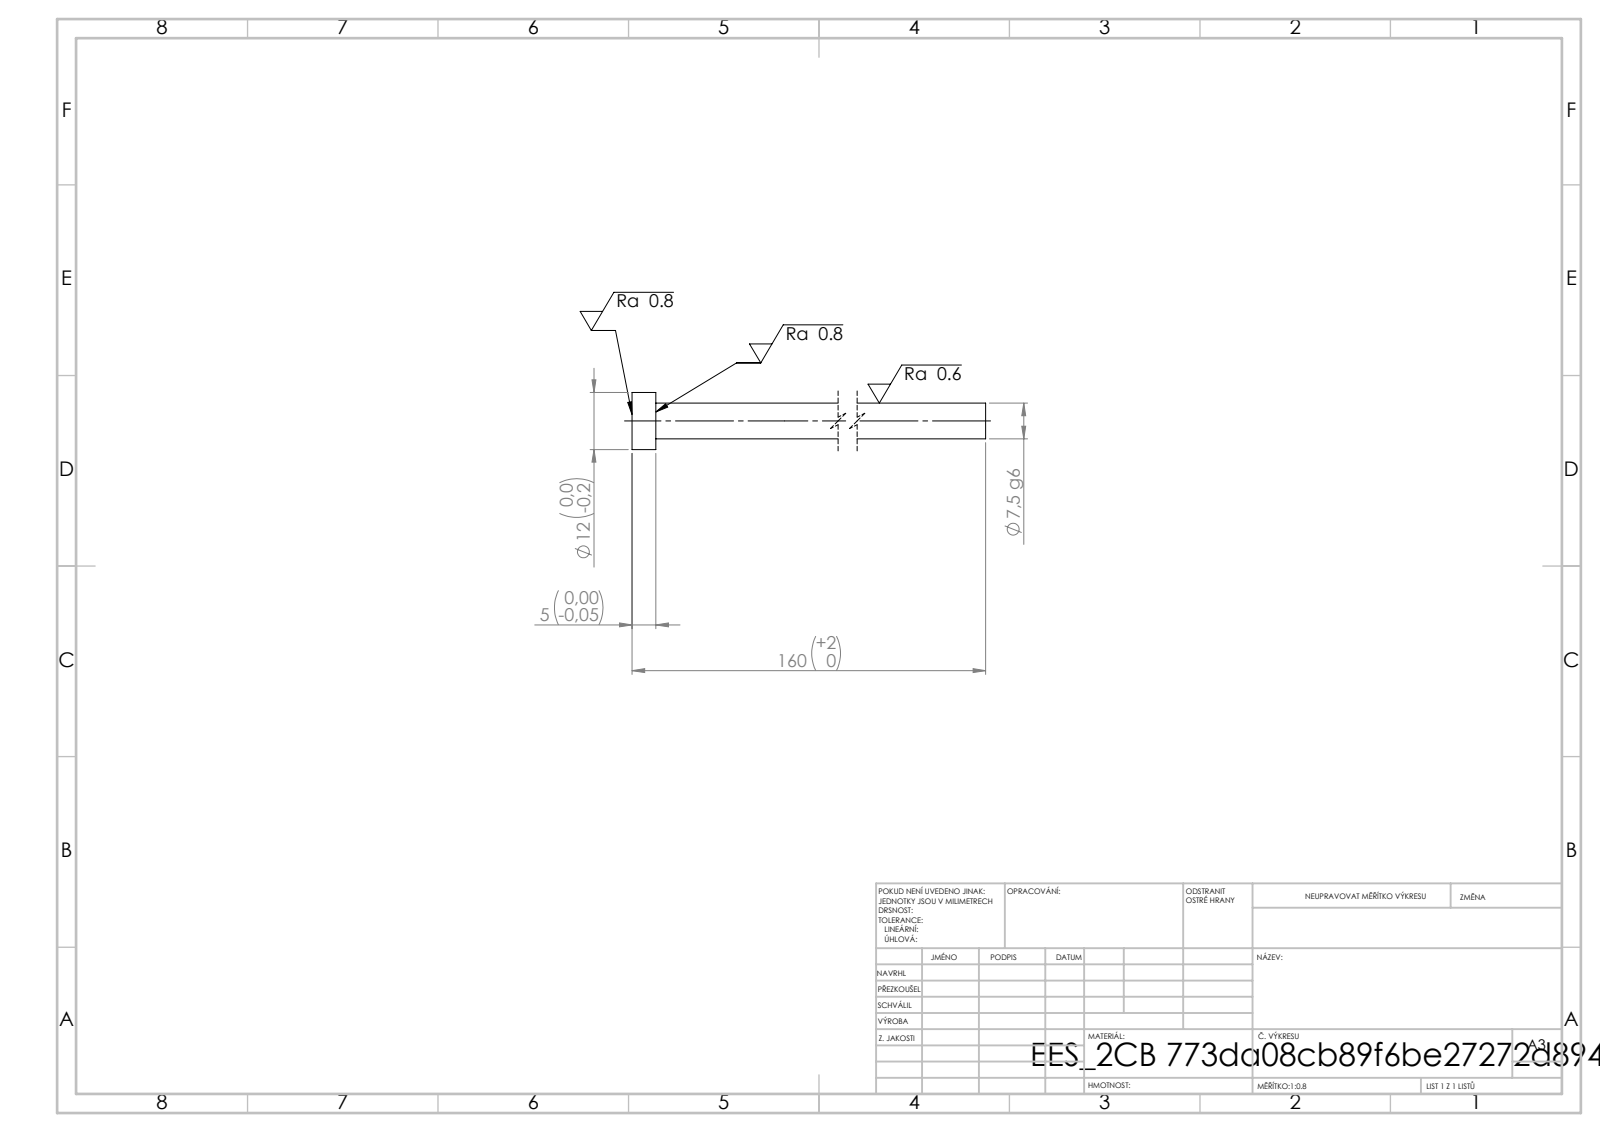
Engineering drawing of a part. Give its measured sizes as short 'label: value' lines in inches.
written by: SolidWorks 2019 (CONFIG_CONTROL_DESIGN)
unit: in
bodies: 1 solid, 7 faces (3 planar, 4 cylindrical, 0 other)
size: 6.299 × 0.472 × 0.472
volume: 0.452 in³; area: 6.304 in²
bosses: 1× ⌀0.472, 1× ⌀0.295
face distances: 0.197, 6.299, 6.102
